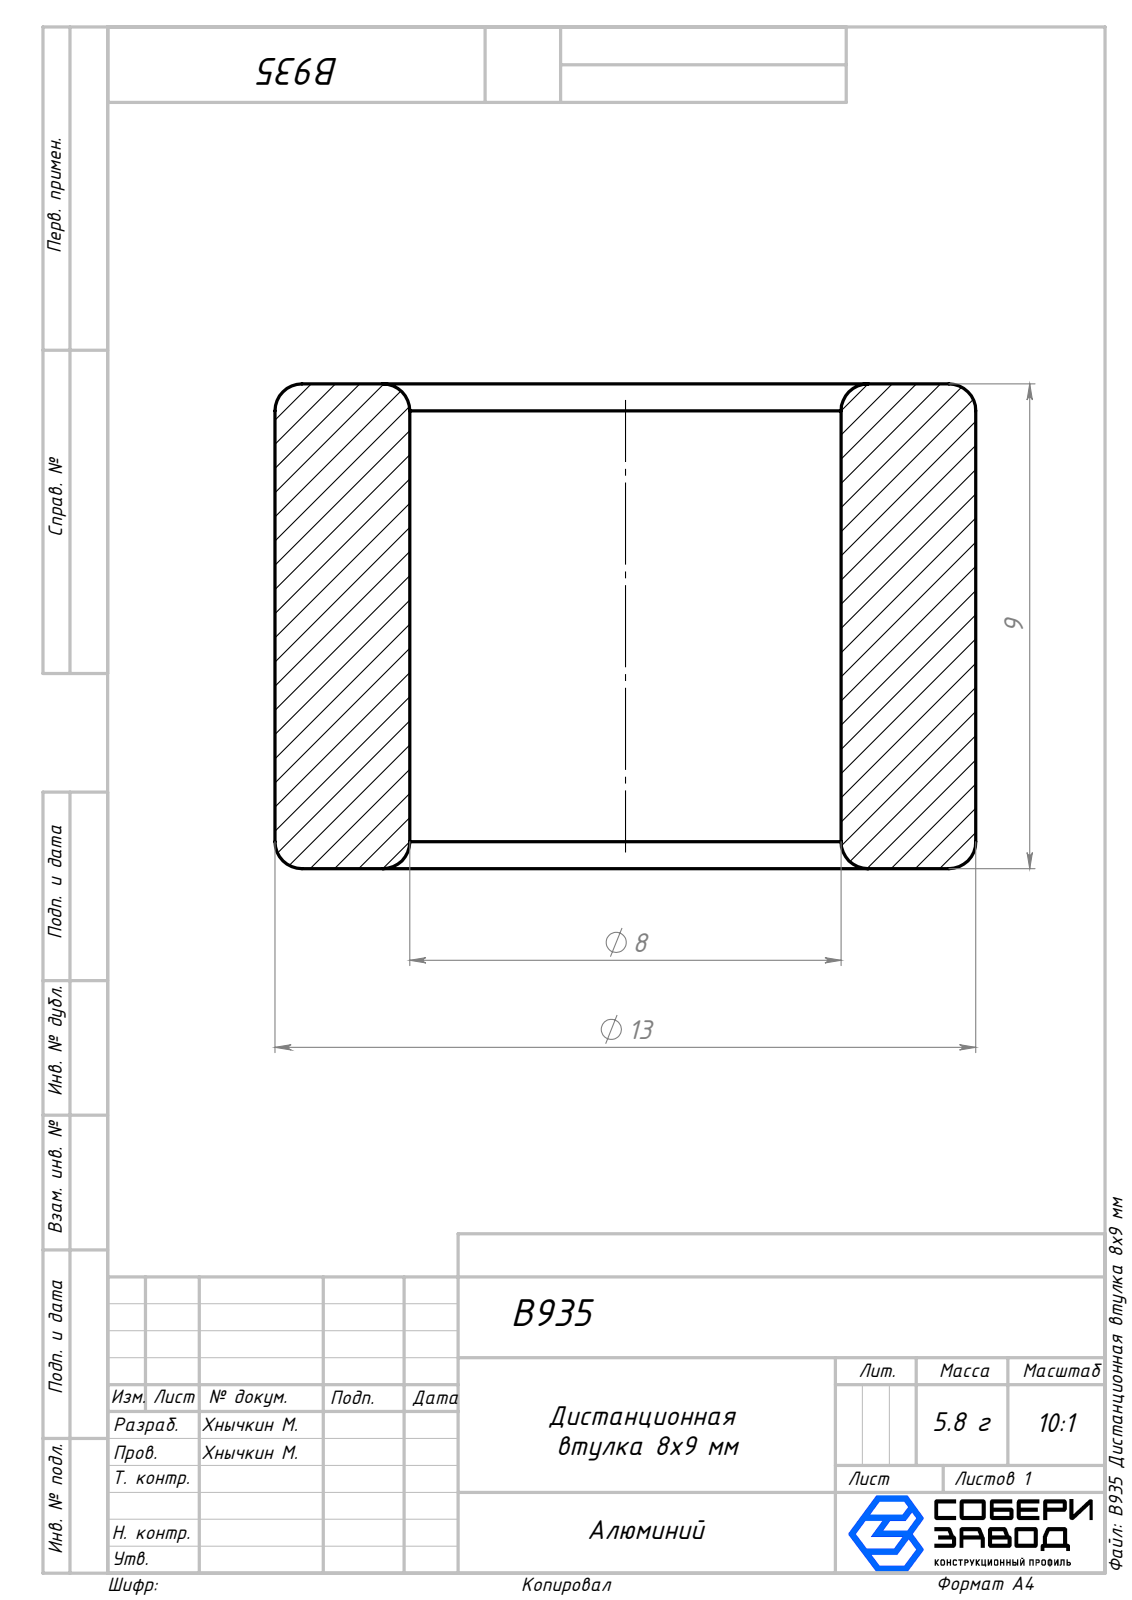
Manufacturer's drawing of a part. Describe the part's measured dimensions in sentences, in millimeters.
The part is named "B935 Дистанционная втулка 8x9 мм". Its 3-D file was written by "SolidWorks 2026 (AUTOMOTIVE_DESIGN)". It is 1 solid with 14 faces: 2 planar, 4 cylindrical and 8 other. Overall it measures 13 by 13 by 9 millimeters. Its volume is 735 cubic millimeters and its surface area 730 square millimeters. Round holes: 1 of diameter 8. Round bosses or shafts: 1 of diameter 13. The main face-to-face distances are 9.
